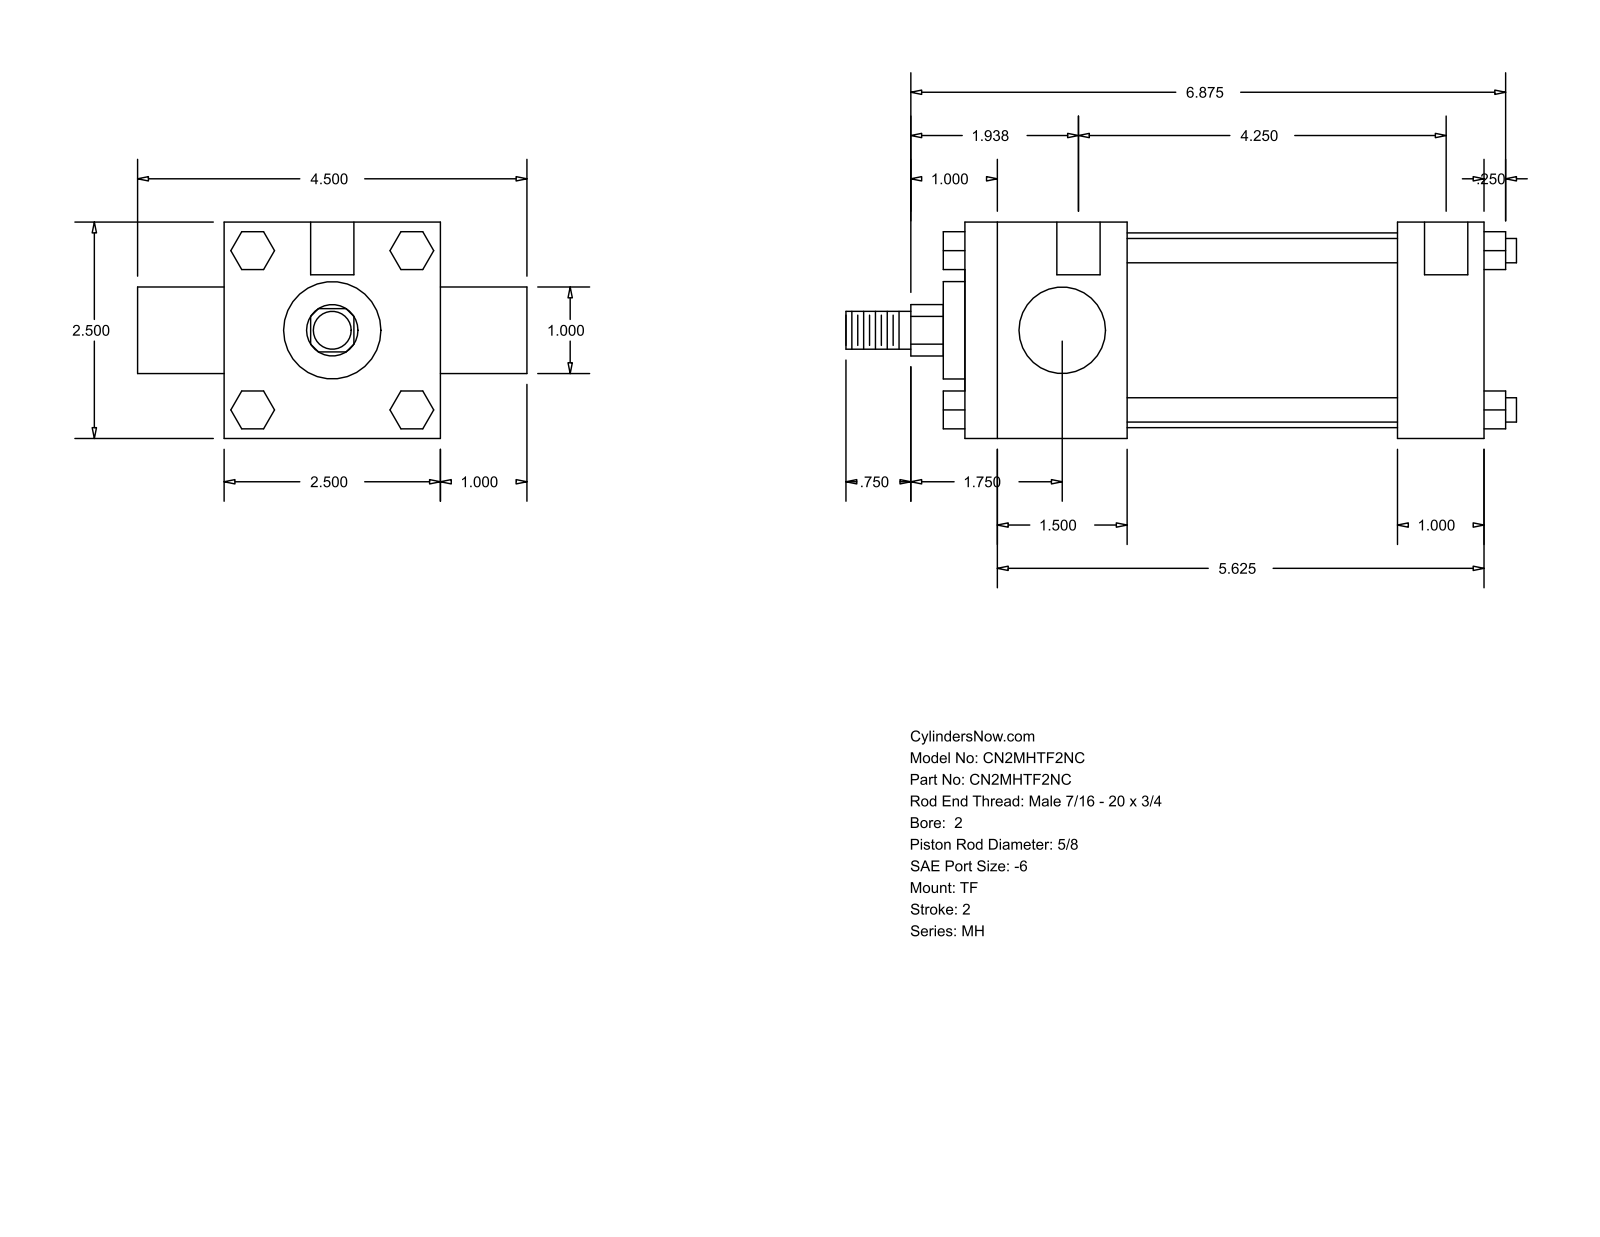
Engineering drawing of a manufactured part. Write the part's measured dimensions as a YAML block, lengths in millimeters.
part_name: "MH_TF__0200_0.625"
step_written_by: "GSSL Pune (CONFIG_CONTROL_DESIGN)"
units: millimeters
bodies: {solids: 0, faces: 120, planar: 92, cylindrical: 28, other: 0}
overall_size: [196.85, 114.3, 63.5]
round_holes:
  - {diameter: 5.56, count: 3}
  - {diameter: 12.7, count: 2}
round_bosses_or_shafts:
  - {diameter: 7.14, count: 4}
  - {diameter: 57.15, count: 1}
  - {diameter: 28.57, count: 1}
  - {diameter: 25.4, count: 1}
  - {diameter: 15.88, count: 1}
  - {diameter: 11.11, count: 1}
partial_cylinders:
  - {radius: 7.54, count: 1}
face_to_face_distances: [63.5, 152.4, 25.4, 47.62, 127, 79.38, 104.78, 88.9, 6.35, 53.97]
hole_center_spacings: [3.18, 4.76, 107.95, 111.13, 112.71, 115.89]
